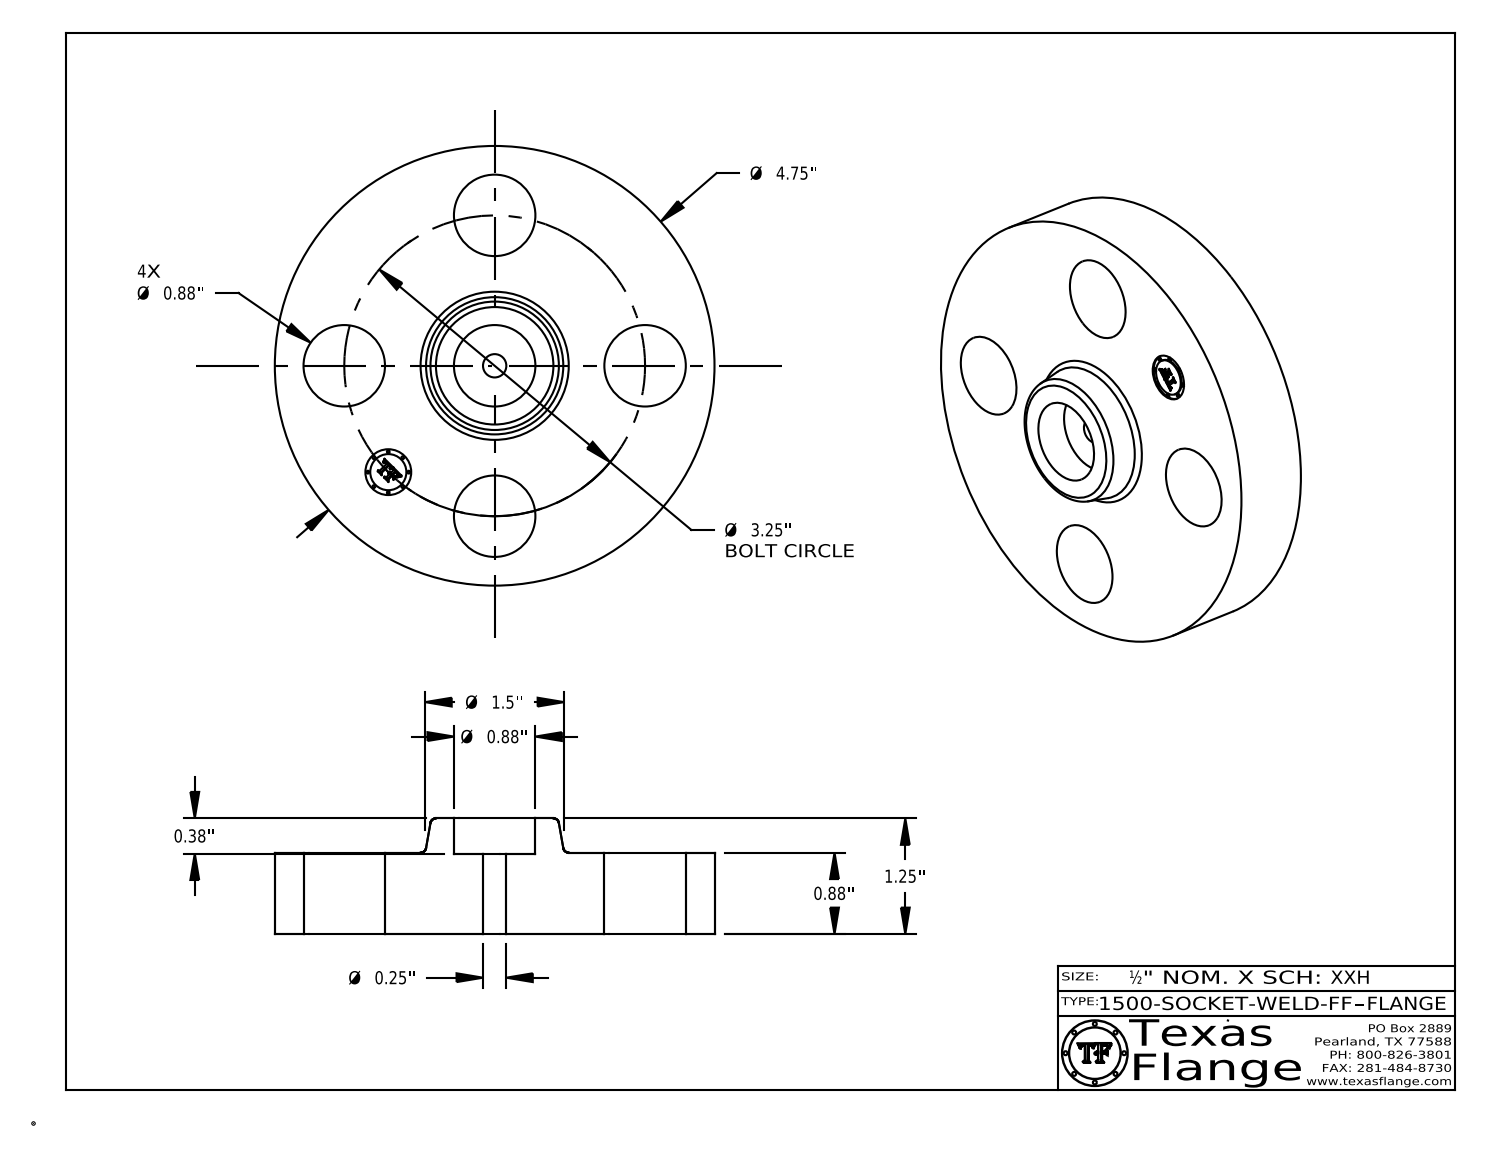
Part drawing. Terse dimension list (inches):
name: 1500-SOCKET-WELD-FF
written by: CATIA V5 STEP AP214 (AUTOMOTIVE_DESIGN)
unit: in
bodies: 1 solid, 409 faces (369 planar, 34 cylindrical, 6 other)
size: 4.75 × 4.75 × 1.25
volume: 13.78 in³; area: 56.42 in²
holes: 5× ⌀0.88, 1× ⌀0.252, 1× ⌀0.495
bosses: 8× ⌀0.03, 1× ⌀4.75, 1× ⌀0.39
face distances: 0.88, 1.25, 0.37, 0.87, 0.38, 0.865, 0.015, 0.385, 0.148, 0.144
hole spacings: 1.625, 2.298, 1.244, 3.003, 3.25
